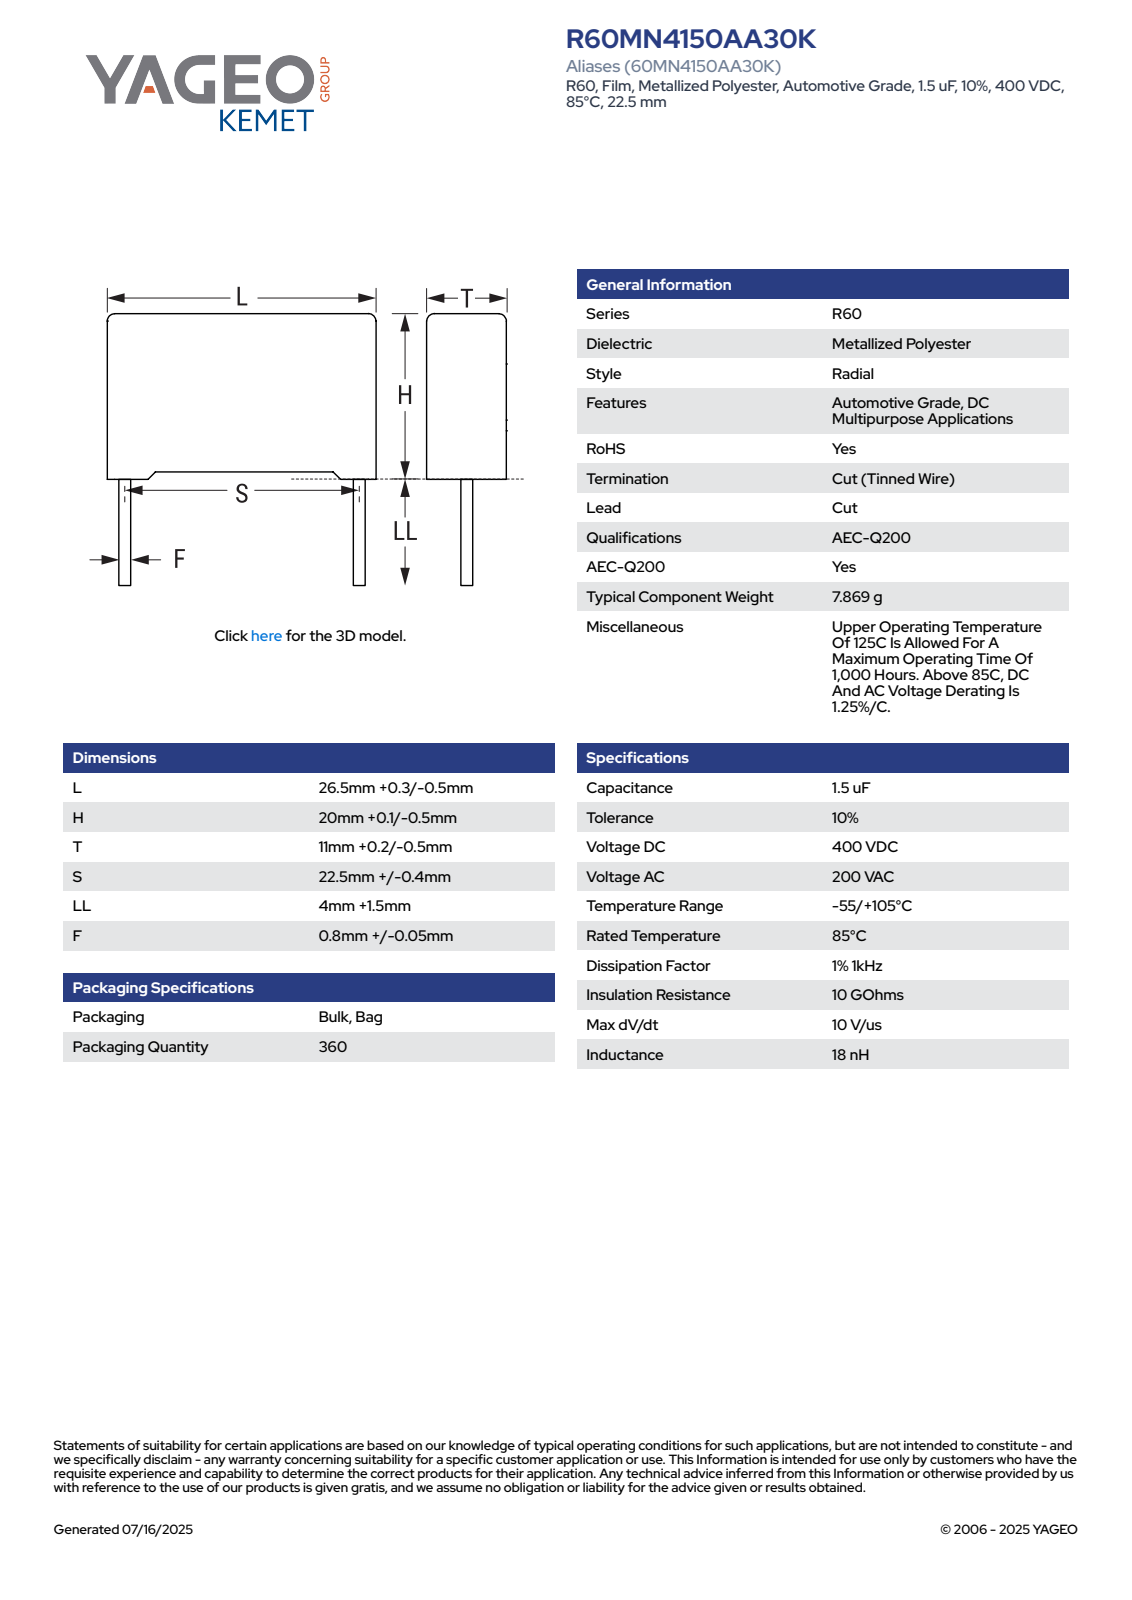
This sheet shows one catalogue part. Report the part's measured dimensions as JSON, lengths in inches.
{"part_name": "CFR_RB2_26.5X20X11_L26.8H20.1T11.2S22.5LL5.5F0.85", "step_written_by": "SolidWorks 2021 (AUTOMOTIVE_DESIGN)", "units": "inches", "bodies": {"solids": 4, "faces": 85, "planar": 77, "cylindrical": 8, "other": 0}, "overall_size": [1.055, 1.008, 0.441], "volume_in3": 0.356, "surface_area_in2": 3.408, "round_bosses_or_shafts": [[0.033, 2]], "partial_cylinders_radius": [[0.02, 4]], "face_to_face_distances": [0.441, 0.762, 1.055, 0.764, 0.03, 0.027, 0.791, 0.035, 1.02, 0.441]}
